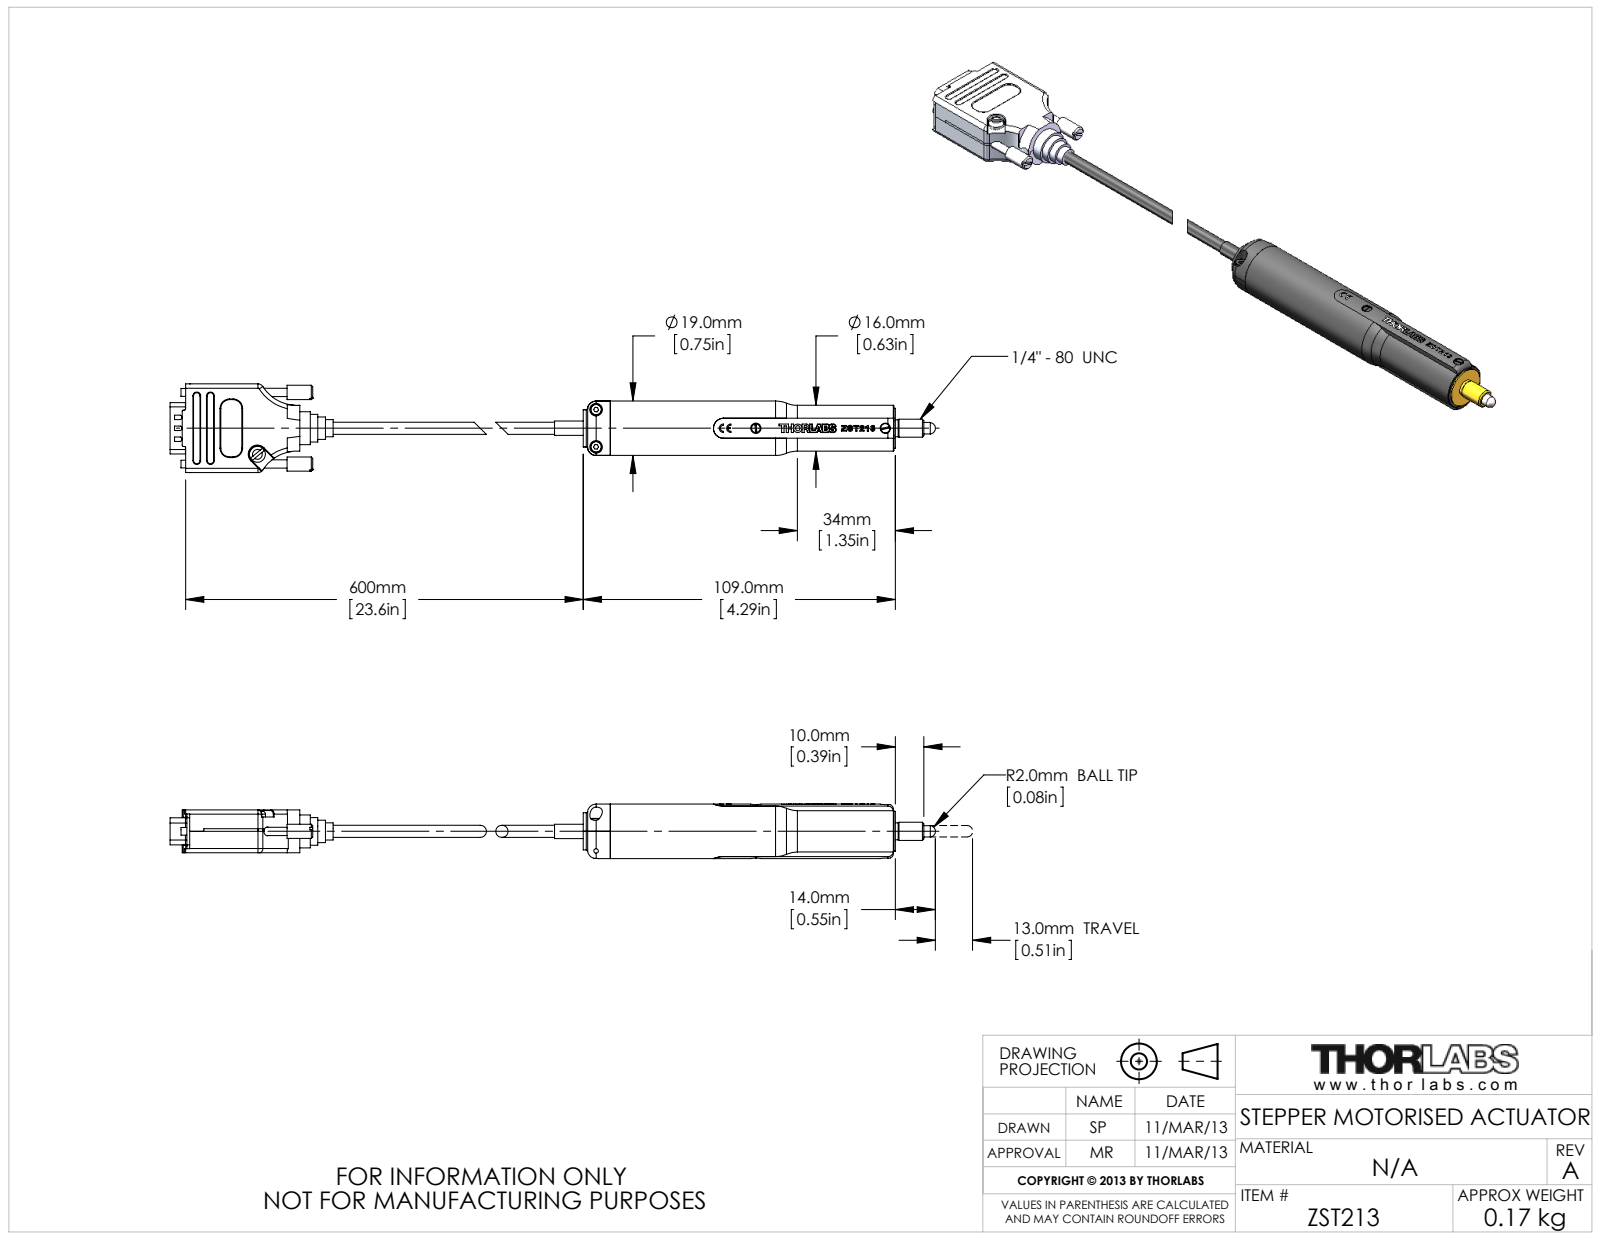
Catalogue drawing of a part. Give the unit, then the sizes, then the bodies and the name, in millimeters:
Units: millimetres
Overall size (bounding box): 280.58 × 31 × 19
Round holes (diameter × count): ⌀1.6 ×3, ⌀3.05 ×2, ⌀3.6 ×2, ⌀4.4 ×2, ⌀4.3 ×1
Round bosses / shafts (diameter × count): ⌀0.99 ×15, ⌀5.56 ×2, ⌀4.97 ×2, ⌀3.8 ×2, ⌀2.89 ×2, ⌀2.73 ×2, ⌀19 ×1, ⌀14 ×1
Partial cylindrical surfaces — rounded edges, fillets, slot ends (radius × count): R0.25 ×20, R1.52 ×12, R0.38 ×4, R1.1 ×4, R2.03 ×4, R3.05 ×4, R0.51 ×3, R1.02 ×2
Main face-to-face distances: 1.39, 13.59, 12.2, 14.98, 0.35, 12, 19, 14.63, 1.04, 13.24
Hole centre spacings: 6.5, 12.5, 56.18, 101.21, 13, 25, 45.2, 55.8
Bodies: 0 solids, 509 faces (180 planar, 212 cylindrical, 117 other)
Part name (STEP PRODUCT): ZST213
STEP written by: SolidWorks 2012 (AUTOMOTIVE_DESIGN)
